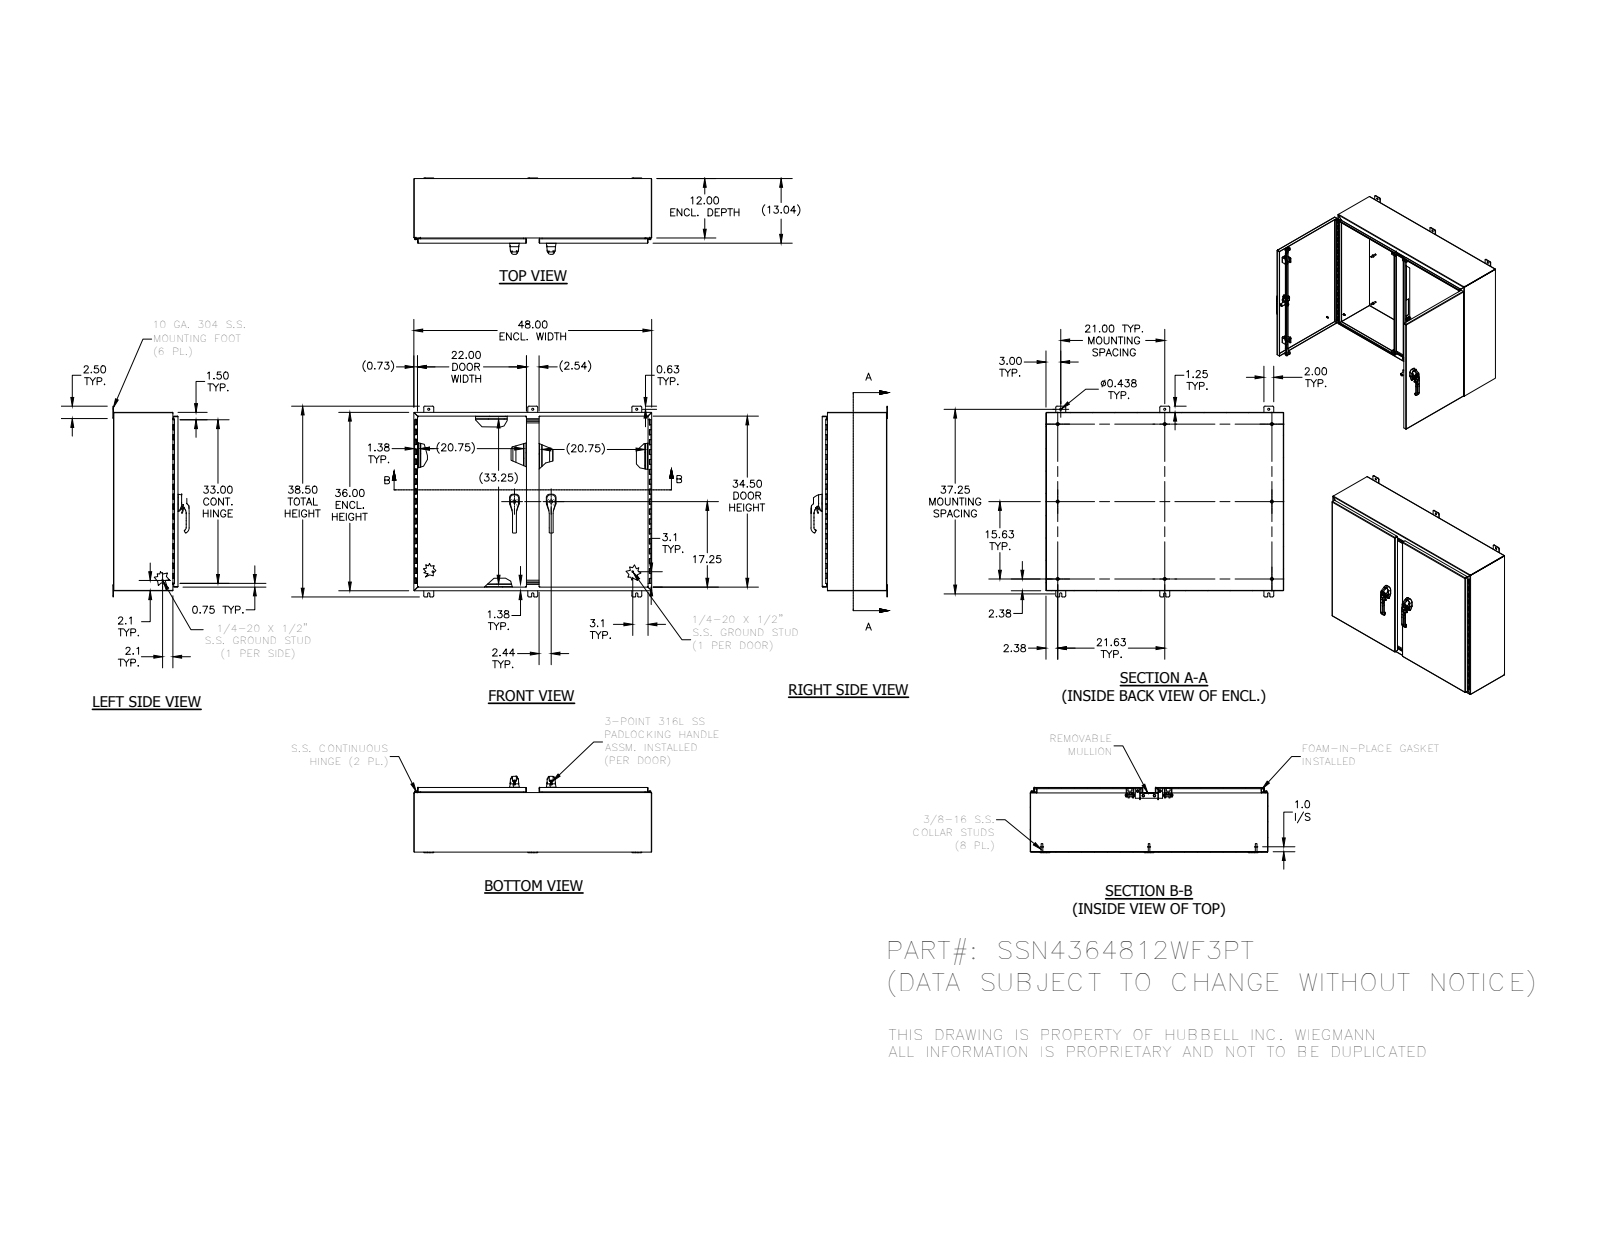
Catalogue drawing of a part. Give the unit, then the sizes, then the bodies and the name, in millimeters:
Units: millimetres
Overall size (bounding box): 1219.2 × 977.9 × 391.4
Round holes (diameter × count): ⌀6.7 ×12, ⌀4.7 ×8, ⌀5.4 ×6, ⌀7.1 ×6, ⌀11.1 ×6, ⌀5 ×4, ⌀6.4 ×4, ⌀7.1 ×4, ⌀8 ×4, ⌀10.2 ×4, ⌀10.2 ×4, ⌀11.4 ×4
Round bosses / shafts (diameter × count): ⌀6.4 ×9, ⌀15.9 ×8, ⌀8.4 ×8, ⌀13.5 ×6, ⌀6 ×5, ⌀13.5 ×4, ⌀11.1 ×4, ⌀11 ×4
Partial cylindrical surfaces — rounded edges, fillets, slot ends (radius × count): R0.5 ×317, R0.3 ×221, R0.5 ×39, R0.8 ×33, R3.2 ×31, R1.3 ×30, R6.4 ×30, R2 ×25
Main face-to-face distances: 1.9, 2.4, 328.7, 326.8, 331.1, 329.2, 912.5, 1217.3, 302.9, 910.6
Hole centre spacings: 9.7, 19.3, 188.4, 12.5, 12.5, 22.5, 31.4, 35
Volume: 8 859 000 mm³ · Surface area: 8 633 000 mm²
Bodies: 127 solids, 6644 faces (2382 planar, 2742 cylindrical, 1520 other)
Part name (STEP PRODUCT): 1091-903_AF0_1; HFW303115; SPACER; HFW372182 (+8 more)
STEP written by: SolidWorks 2014 (AUTOMOTIVE_DESIGN)
